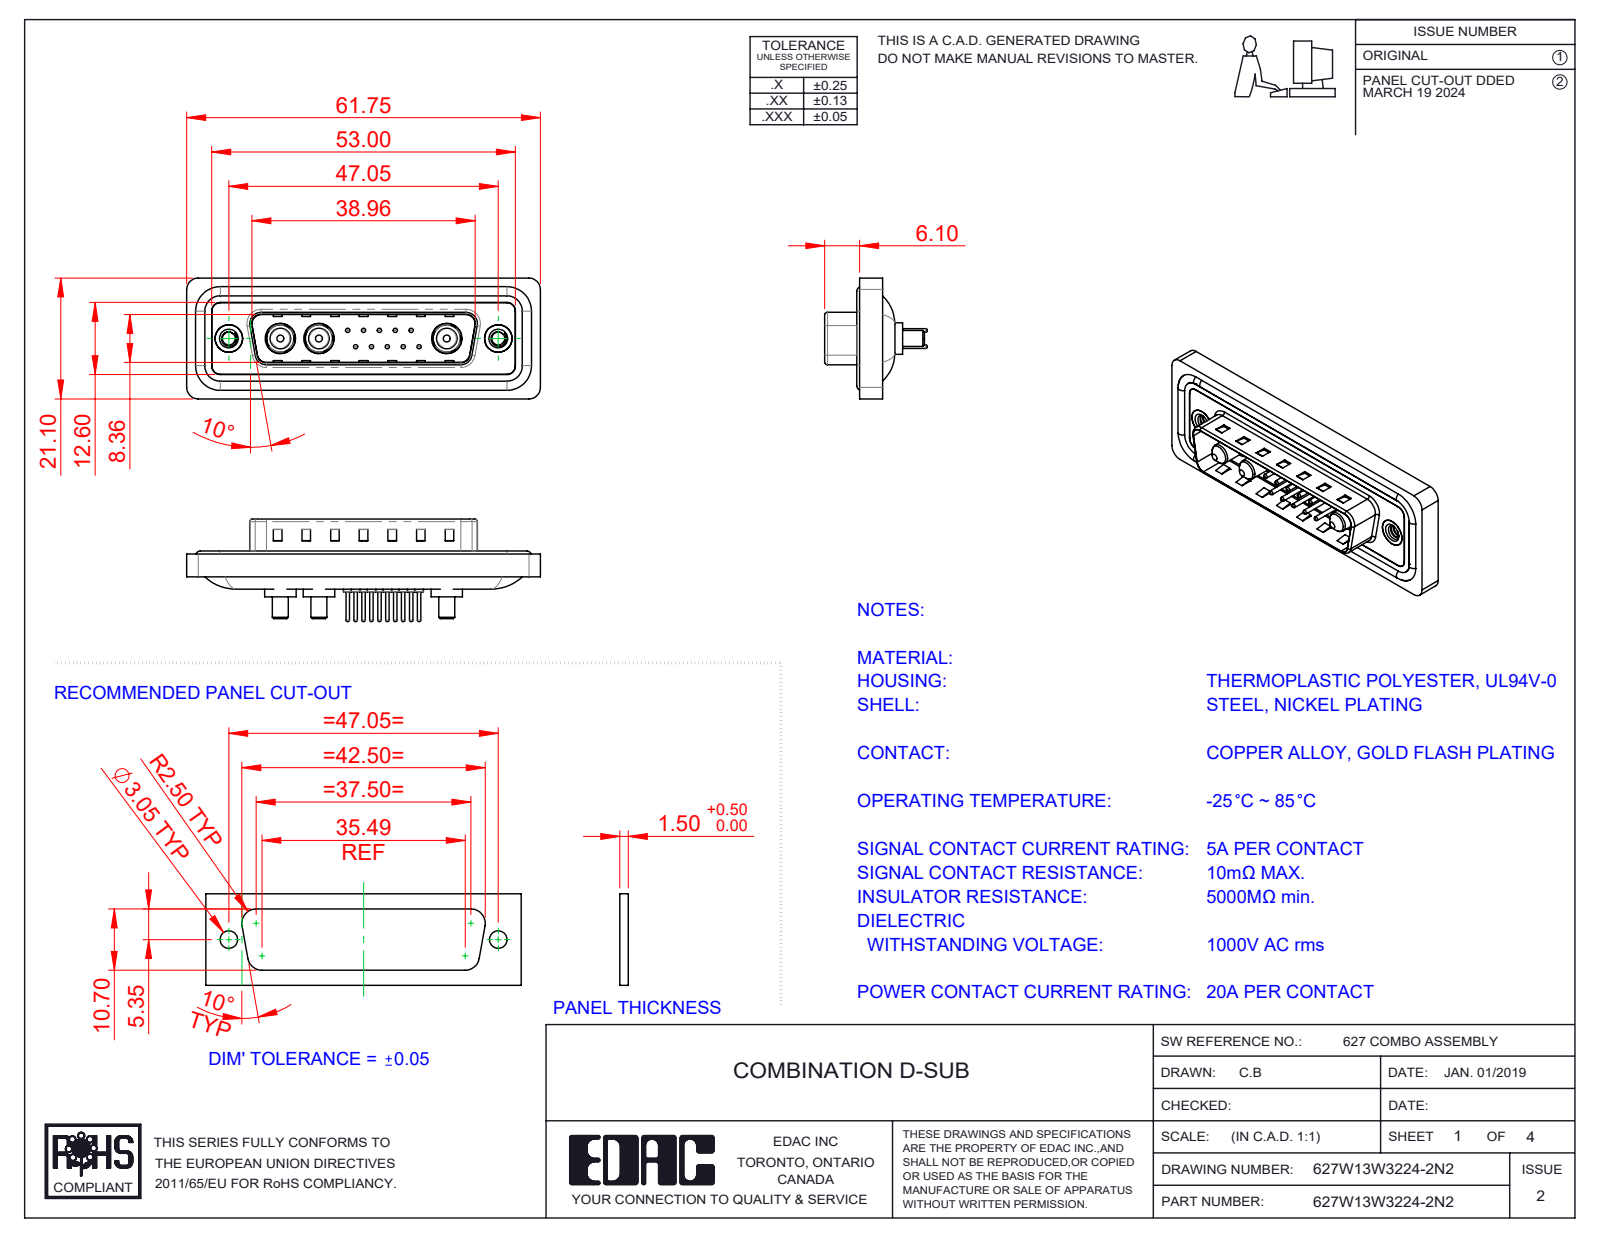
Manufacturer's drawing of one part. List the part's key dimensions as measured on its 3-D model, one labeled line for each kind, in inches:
Part name (STEP PRODUCT): 627Combo Threaded Rivet_2; 627Combo Contact Row 2_24; 627Combo Shell Front_25 Contacts; Power Pin_20A S (+5 more)
STEP written by: SolidWorks 2023 (CONFIG_CONTROL_DESIGN)
Units: inches
Bodies: 23 solids, 970 faces (309 planar, 385 cylindrical, 276 other)
Overall size (bounding box): 2.431 × 0.831 × 0.705
Volume: 0.448 in³ · Surface area: 18.41 in²
Round holes (diameter × count): ⌀0.03 ×10, ⌀0.063 ×10, ⌀0.079 ×10, ⌀0.191 ×3, ⌀0.209 ×3, ⌀0.089 ×2, ⌀0.157 ×2, ⌀0.189 ×2, ⌀0.197 ×2
Round bosses / shafts (diameter × count): ⌀0.059 ×10, ⌀0.024 ×10, ⌀0.063 ×4, ⌀0.217 ×3, ⌀0.205 ×3, ⌀0.187 ×3, ⌀0.148 ×3, ⌀0.142 ×3
Partial cylindrical surfaces — rounded edges, fillets, slot ends (radius × count): R0.059 ×22, R0.079 ×18, R0.02 ×8, R0.063 ×8, R0.01 ×4, R0.024 ×4, R0.026 ×4, R0.035 ×4
Main face-to-face distances: 0.016, 0.059, 0.043, 0.063, 0.02, 0.122, 0.114, 0.032, 0.377, 0.161
Hole centre spacings: 0.124, 0.109, 0.198, 0.218, 0.295, 0.198, 0.327, 0.398
